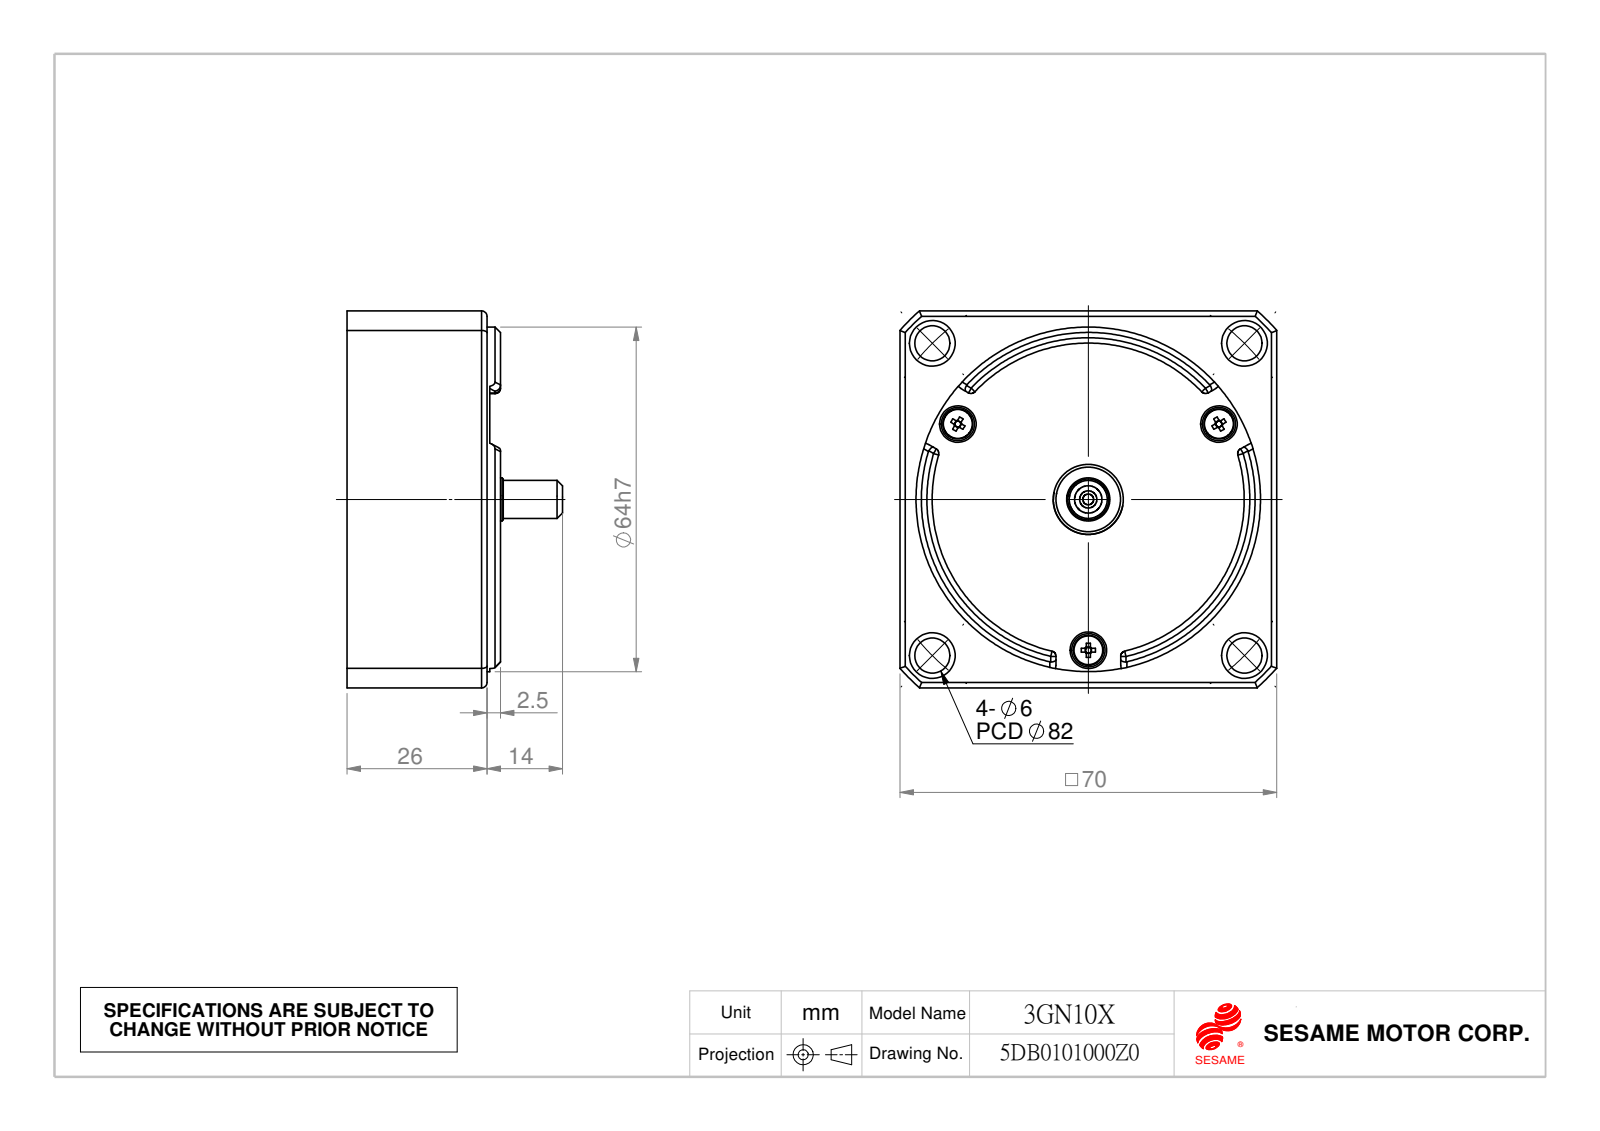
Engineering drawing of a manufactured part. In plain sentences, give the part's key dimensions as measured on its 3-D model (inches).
The part is named "3GN10XK-2A(模型)_Default; G364-M齒箱模型_加工圖; FT250; JIS B 1111 Cross recessed pan head screw - M3 x 4 - Z --4N_JIS B 1111 Cross recessed pan head screw - M3 x 4 - Z --4N". Its 3-D file was written by "SolidWorks 2010 (CONFIG_CONTROL_DESIGN)". It is 11 solids with 411 faces: 142 planar, 133 cylindrical and 136 other. Overall it measures 2.756 by 2.756 by 1.575 inches. Its volume is 6.44 cubic inches and its surface area 49.5 square inches. Round holes: 5 of diameter 0.197, 3 of diameter 0.108, 3 of diameter 0.244, 2 of diameter 0.512, 1 of diameter 0.079, 1 of diameter 0.118, 1 of diameter 0.394, 1 of diameter 0.669. Round bosses or shafts: 4 of diameter 0.276, 4 of diameter 0.196, 3 of diameter 0.22, 3 of diameter 0.118, 1 of diameter 2.52, 1 of diameter 2.518, 1 of diameter 0.591, 1 of diameter 0.315. Partial cylindrical surfaces (rounded edges, fillets, slot ends): 16 of radius 0.039, 8 of radius 0.315, 4 of radius 0.236, 1 of radius 1.142, 1 of radius 1.248, 1 of radius 1.259, 1 of radius 1.85. The main face-to-face distances are 0.079, 2.756, 0.827, 0.748, 0.728, 0.807, 0.02, 0.217, 0.295, 1.024. The hole center spacings are 1.102, 1.909, 0.257, 0.863, 1.083, 1.751, 2.007, 0.581.
